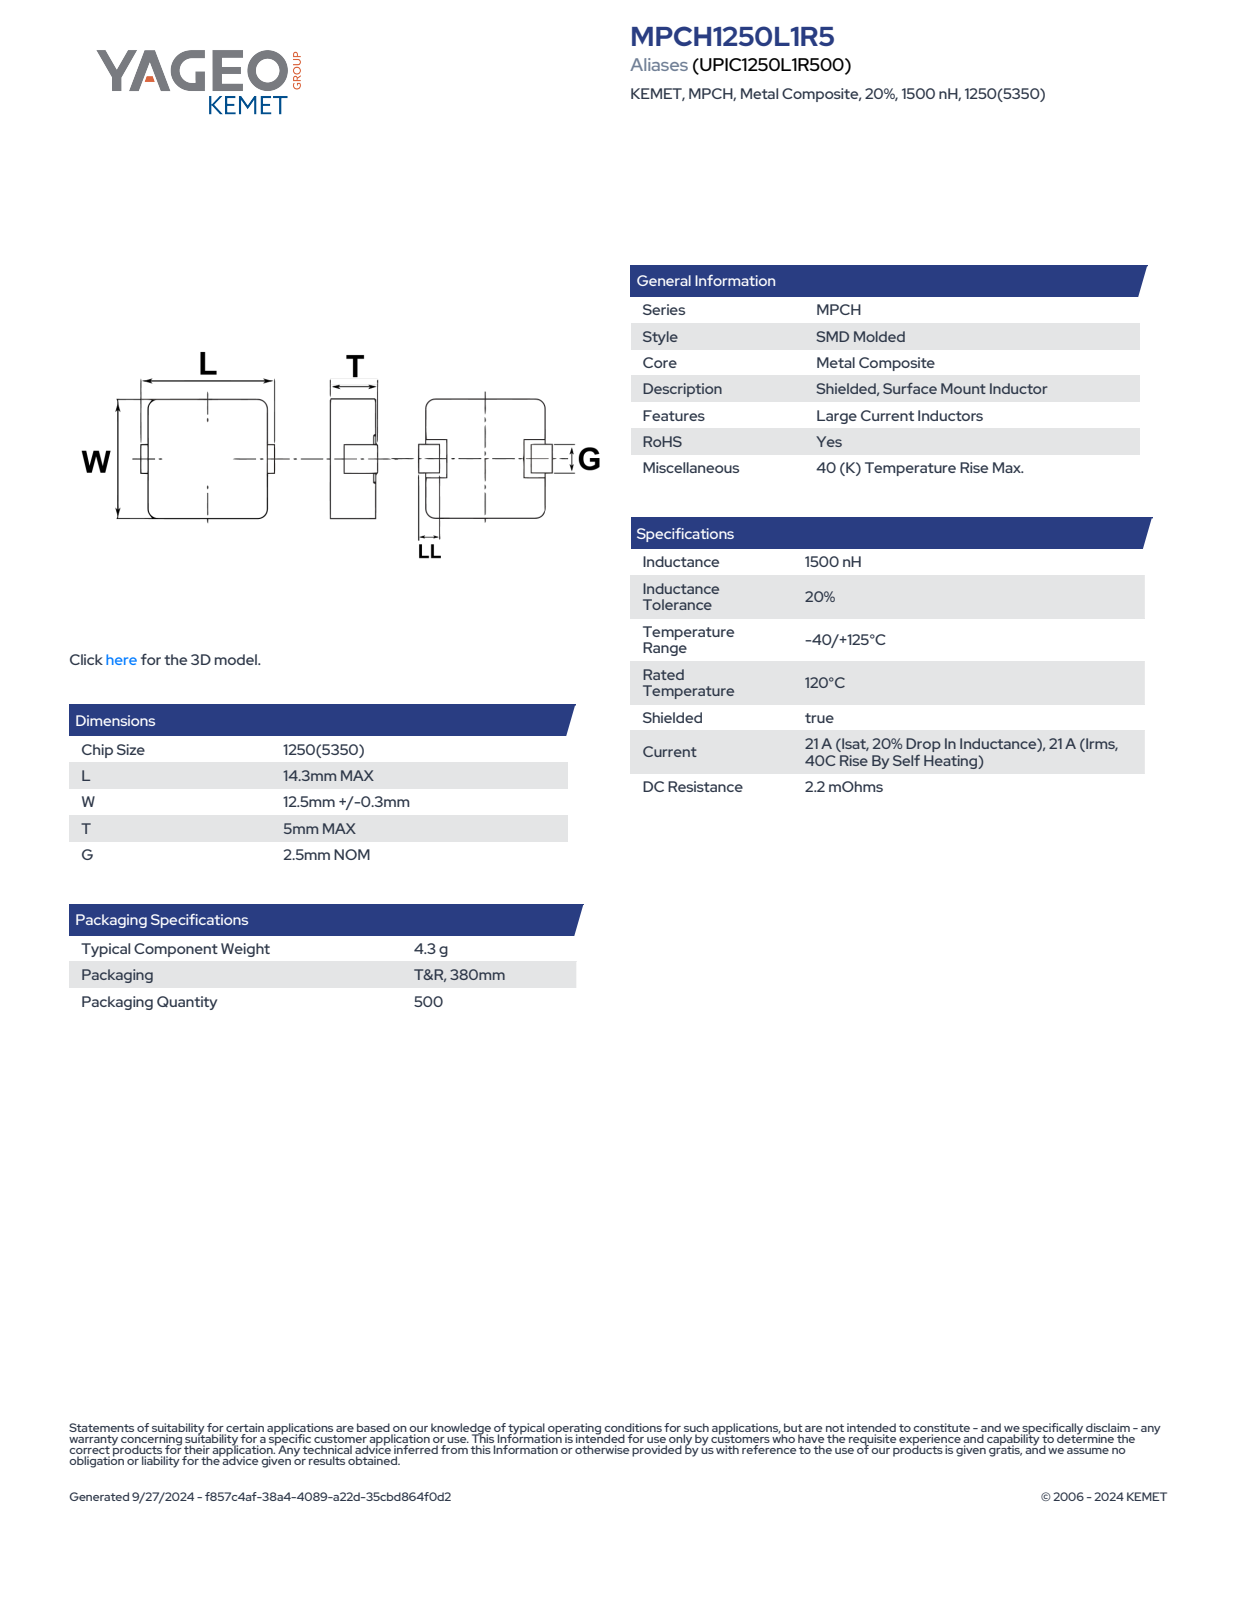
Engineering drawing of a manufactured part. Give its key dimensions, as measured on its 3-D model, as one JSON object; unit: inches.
{"part_name": "IS_MPC_5649_L14.3W12.8T5LL2.2G2.5", "step_written_by": "SolidWorks 2014 (AUTOMOTIVE_DESIGN)", "units": "inches", "bodies": {"solids": 4, "faces": 105, "planar": 93, "cylindrical": 12, "other": 0}, "overall_size": [0.563, 0.504, 0.197], "volume_in3": 0.054, "surface_area_in2": 1.03, "partial_cylinders_radius": [[0.043, 4]], "face_to_face_distances": [0.195, 0.504, 0.547, 0.547, 0.555, 0.546, 0.555, 0.559, 0.551, 0.551]}
